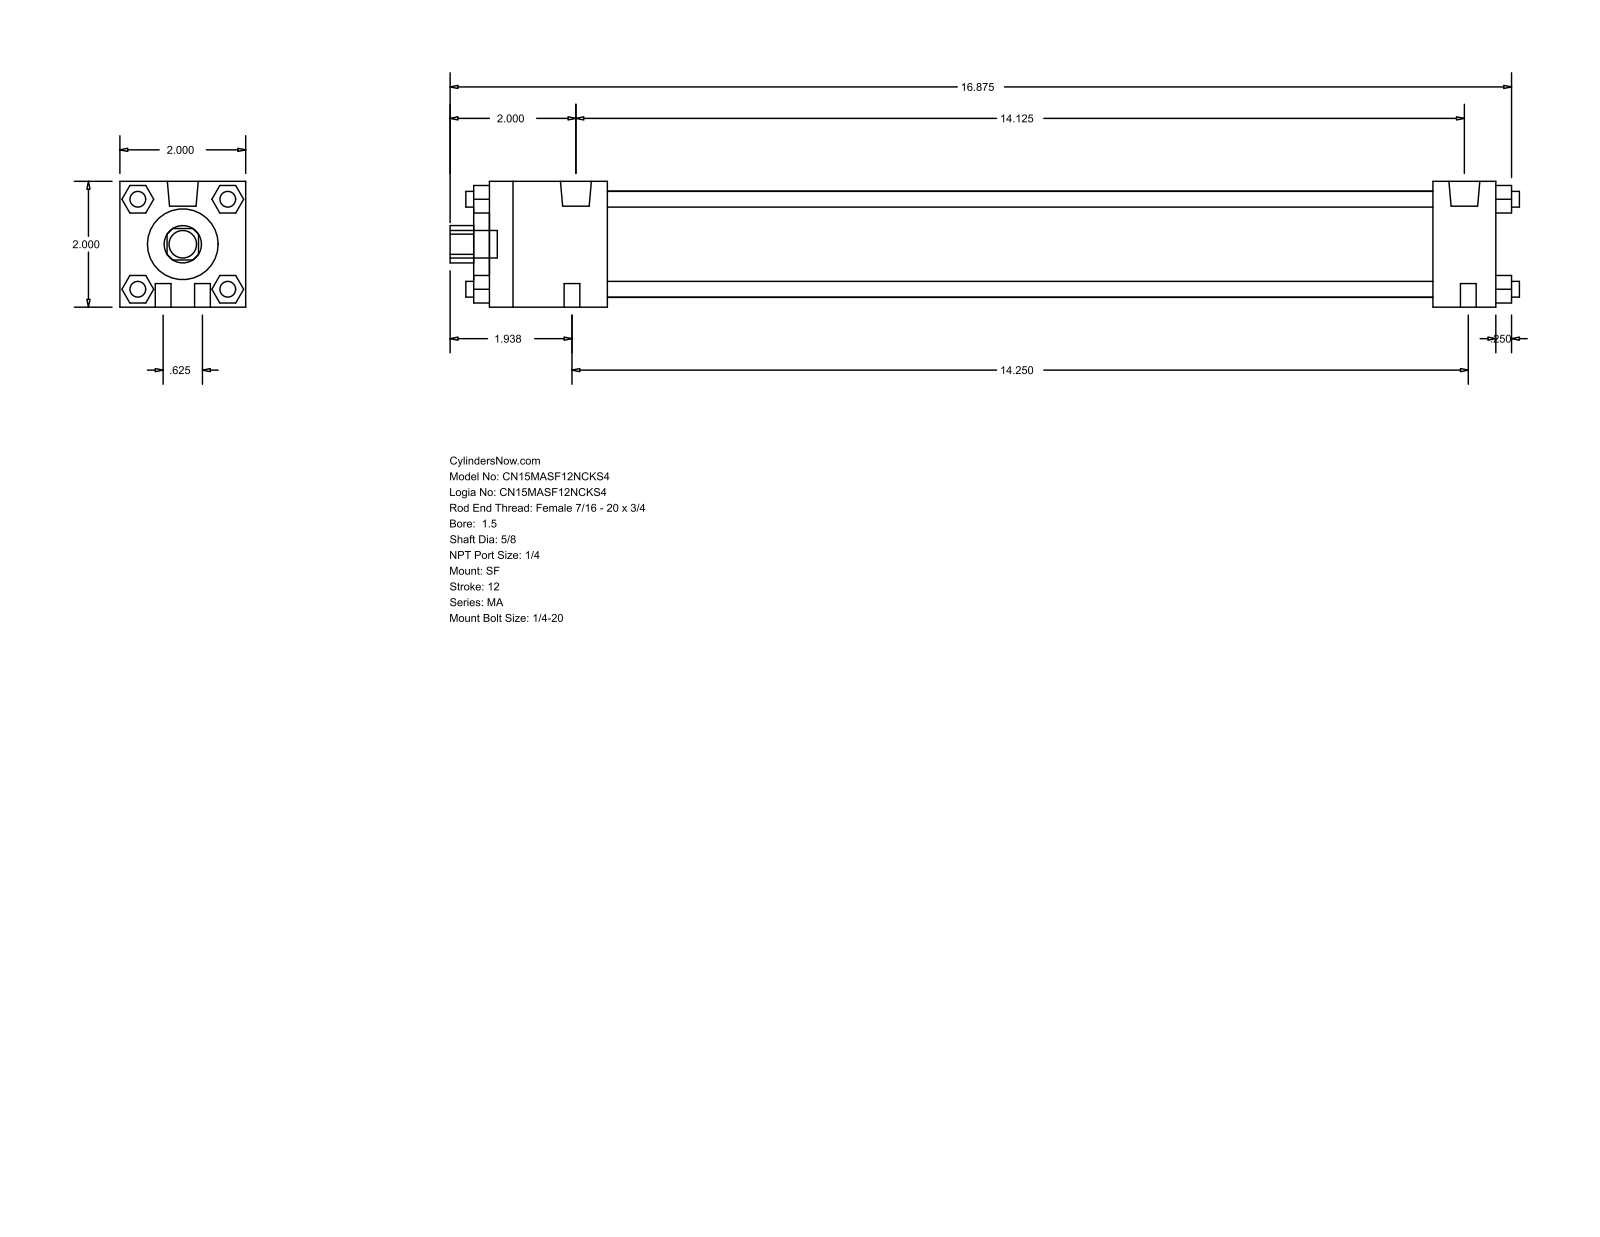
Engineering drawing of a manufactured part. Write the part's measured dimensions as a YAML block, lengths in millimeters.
part_name: "MA_SF__0150_0.625"
step_written_by: "GSSL Pune (CONFIG_CONTROL_DESIGN)"
units: millimeters
bodies: {solids: 0, faces: 124, planar: 94, cylindrical: 30, other: 0}
overall_size: [431.8, 50.8, 50.8]
round_holes:
  - {diameter: 15.88, count: 1}
  - {diameter: 28.57, count: 1}
  - {diameter: 42.93, count: 1}
round_bosses_or_shafts:
  - {diameter: 6.35, count: 8}
  - {diameter: 12.49, count: 2}
  - {diameter: 7.94, count: 2}
  - {diameter: 11.11, count: 1}
partial_cylinders:
  - {radius: 7.54, count: 1}
face_to_face_distances: [50.8, 406.39, 6.35, 412.74, 47.62, 381, 333.38, 358.77, 25.39, 53.97]
